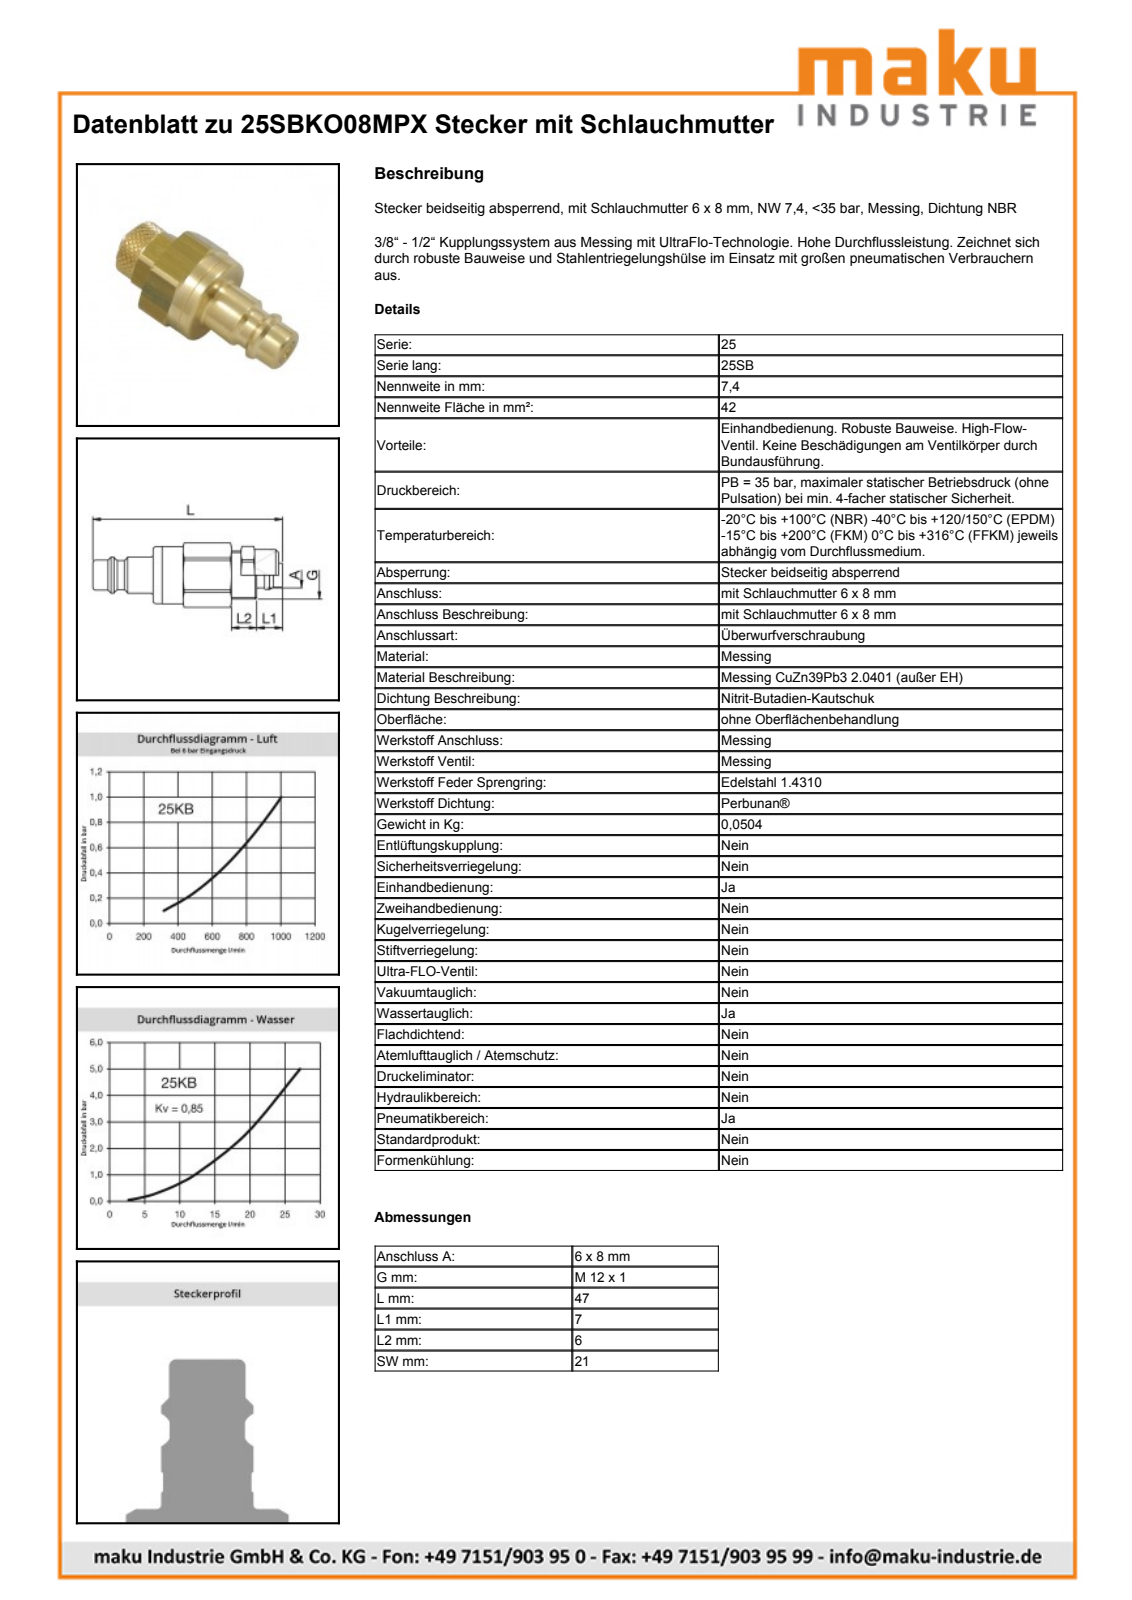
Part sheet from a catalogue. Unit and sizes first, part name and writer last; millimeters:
Units: millimetres
Overall size (bounding box): 47.24 × 23.58 × 22.36
Round holes (diameter × count): ⌀8.25 ×1, ⌀11.15 ×1
Round bosses / shafts (diameter × count): ⌀21 ×1, ⌀14 ×1, ⌀12 ×1, ⌀10.6 ×1, ⌀10 ×1, ⌀9.75 ×1, ⌀6.7 ×1, ⌀6.05 ×1
Partial cylindrical surfaces — rounded edges, fillets, slot ends (radius × count): R7.75 ×1, R11.85 ×1
Main face-to-face distances: 21, 14.14, 14, 21.02, 20, 34.14, 40.14, 20.14, 6, 47.1
Volume: 8 663 mm³ · Surface area: 3 516 mm²
Bodies: 1 solid, 84 faces (20 planar, 24 cylindrical, 40 other)
Part name (STEP PRODUCT): D104874
STEP written by: Autodesk Inventor 2011 (AUTOMOTIVE_DESIGN)
